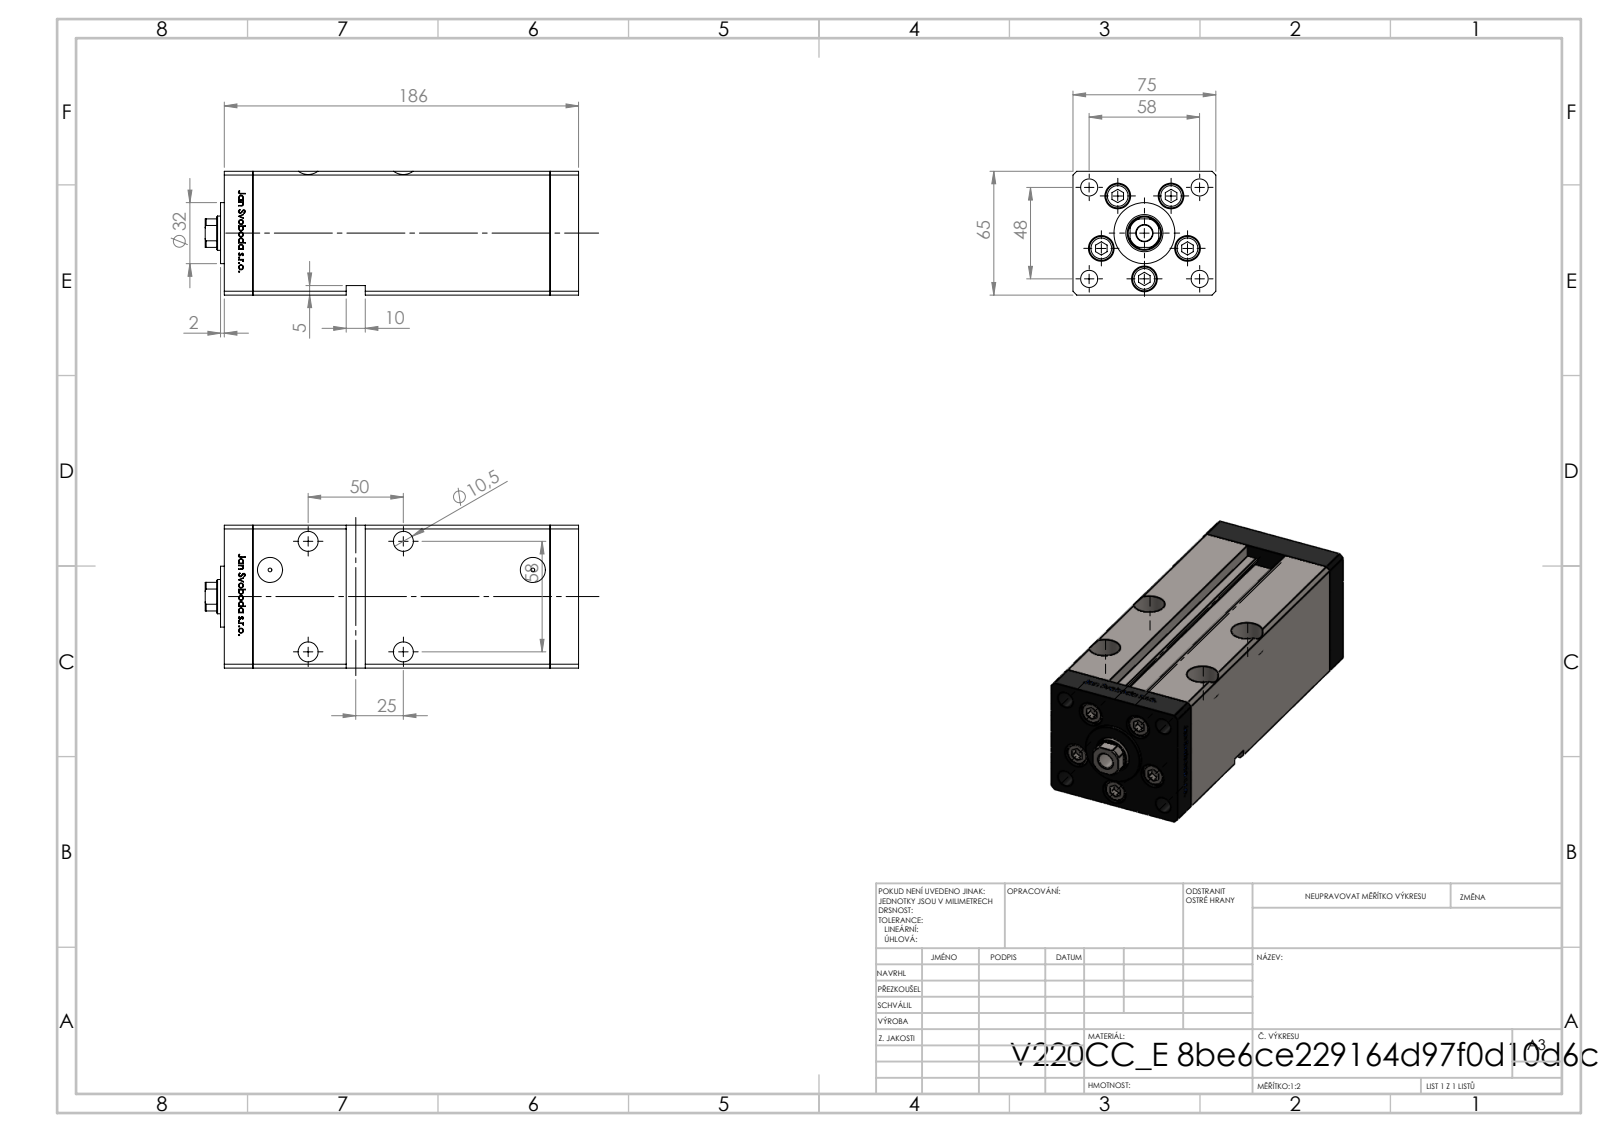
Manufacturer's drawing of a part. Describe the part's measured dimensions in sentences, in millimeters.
The part is named "V220C_VC_E; V220C_FRONT_E; V220C BACK_E; ALLEN BOLT (+1 more)". Its 3-D file was written by "SolidWorks 2019 (CONFIG_CONTROL_DESIGN)". It is 14 solids with 1212 faces: 473 planar, 165 cylindrical and 574 other. Overall it measures 196 by 75 by 65 millimeters. Its volume is 769 603 cubic millimeters and its surface area 146 638 square millimeters. Round holes: 9 of diameter 9, 5 of diameter 13.5, 4 of diameter 10.5, 4 of diameter 16.5, 2 of diameter 2, 2 of diameter 13.16, 1 of diameter 8.5, 1 of diameter 18, 1 of diameter 19.5. Round bosses or shafts: 5 of diameter 12.5, 5 of diameter 8, 1 of diameter 32. Partial cylindrical surfaces (rounded edges, fillets, slot ends): 2 of radius 0.93, 1 of radius 8.5. The main face-to-face distances are 75, 65, 15, 156, 171, 186, 28, 54.5, 10.5, 26.25. The hole center spacings are 24, 37.64, 58, 15.67, 17.22, 27.71, 28.83, 29.
